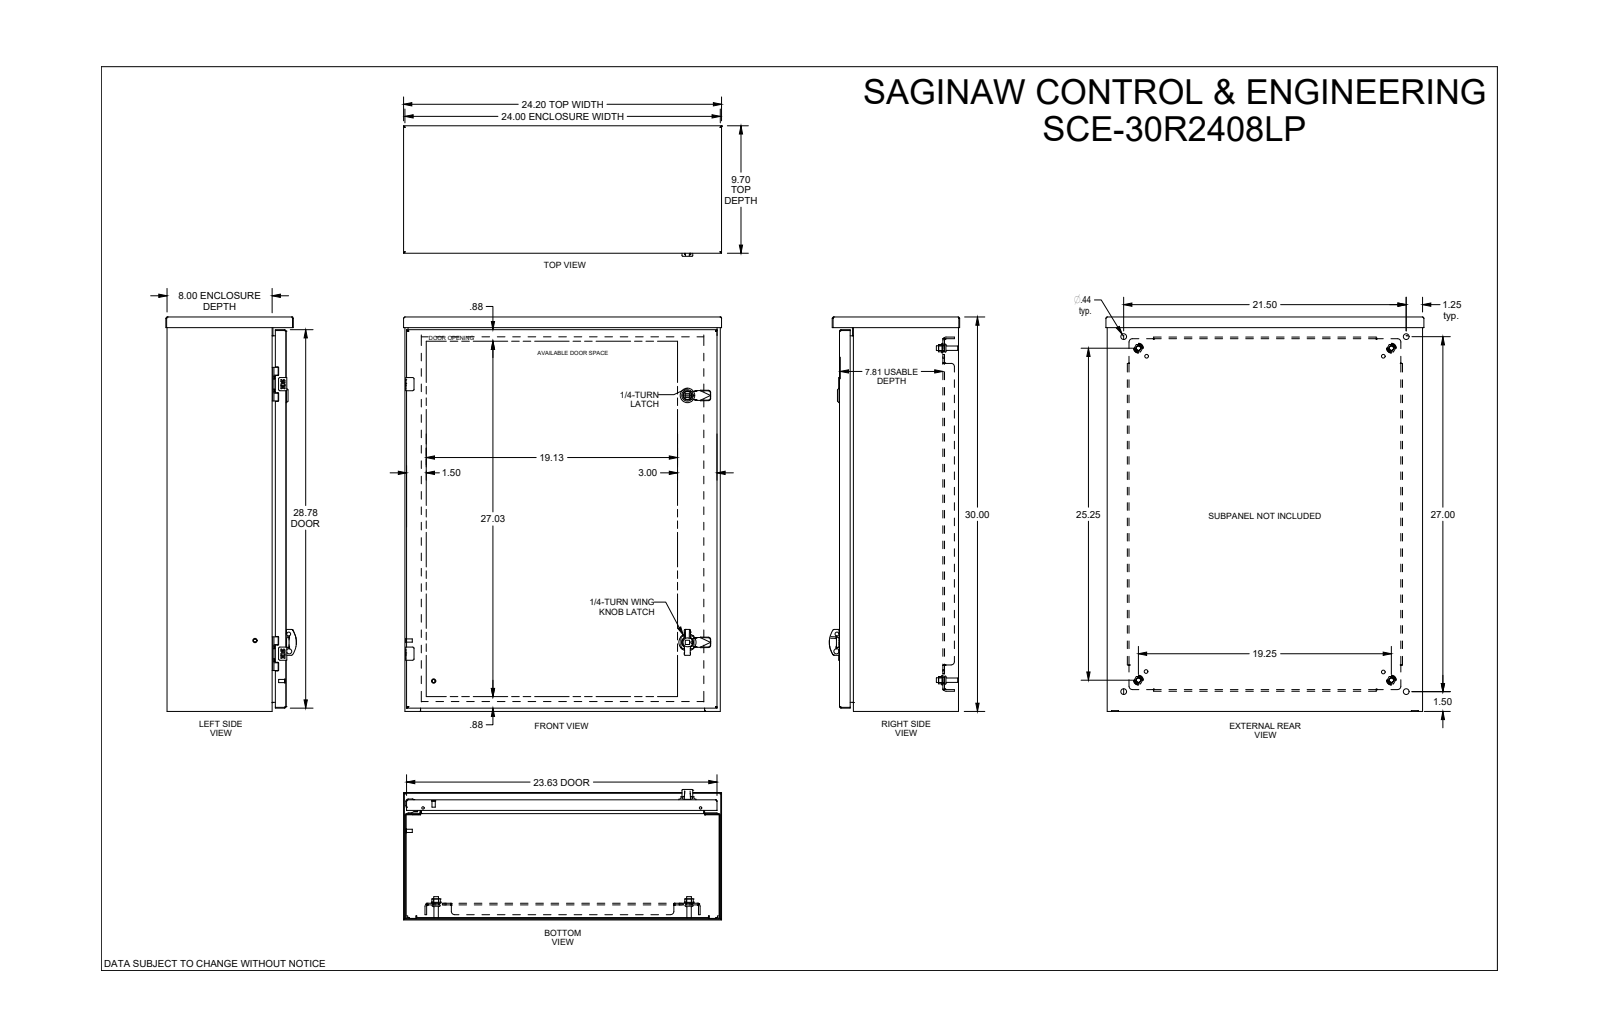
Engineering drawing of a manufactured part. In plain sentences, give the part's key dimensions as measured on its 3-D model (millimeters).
The part is named "SCE-30R2408LP". Its 3-D file was written by "SolidWorks 2019 (CONFIG_CONTROL_DESIGN)". It is 0 solids with 2429 faces: 1160 planar, 823 cylindrical and 446 other. Overall it measures 762 by 614.7 by 252.1 millimeters. Round holes: 4 of diameter 4.4, 4 of diameter 5.2, 4 of diameter 6.2, 4 of diameter 6.8, 4 of diameter 7.1, 4 of diameter 9.3, 4 of diameter 9.5, 4 of diameter 11.1, 4 of diameter 12.7, 2 of diameter 1, 2 of diameter 4, 2 of diameter 4.8. Round bosses or shafts: 6 of diameter 4.3, 4 of diameter 9.3, 4 of diameter 8.4, 4 of diameter 6.4, 4 of diameter 6.1, 3 of diameter 5, 2 of diameter 22, 2 of diameter 20.4. Partial cylindrical surfaces (rounded edges, fillets, slot ends): 72 of radius 0.4, 60 of radius 0.3, 26 of radius 0.3, 24 of radius 0.5, 23 of radius 2.8, 22 of radius 1.5, 19 of radius 1.3, 15 of radius 0.8. The main face-to-face distances are 1.5, 1.5, 226.9, 228.4, 229.9, 228.4, 3.2, 25.4, 201.5, 30.1. The hole center spacings are 520.7, 0.6, 12.5, 22.2, 25, 518, 58.3, 473.5.
